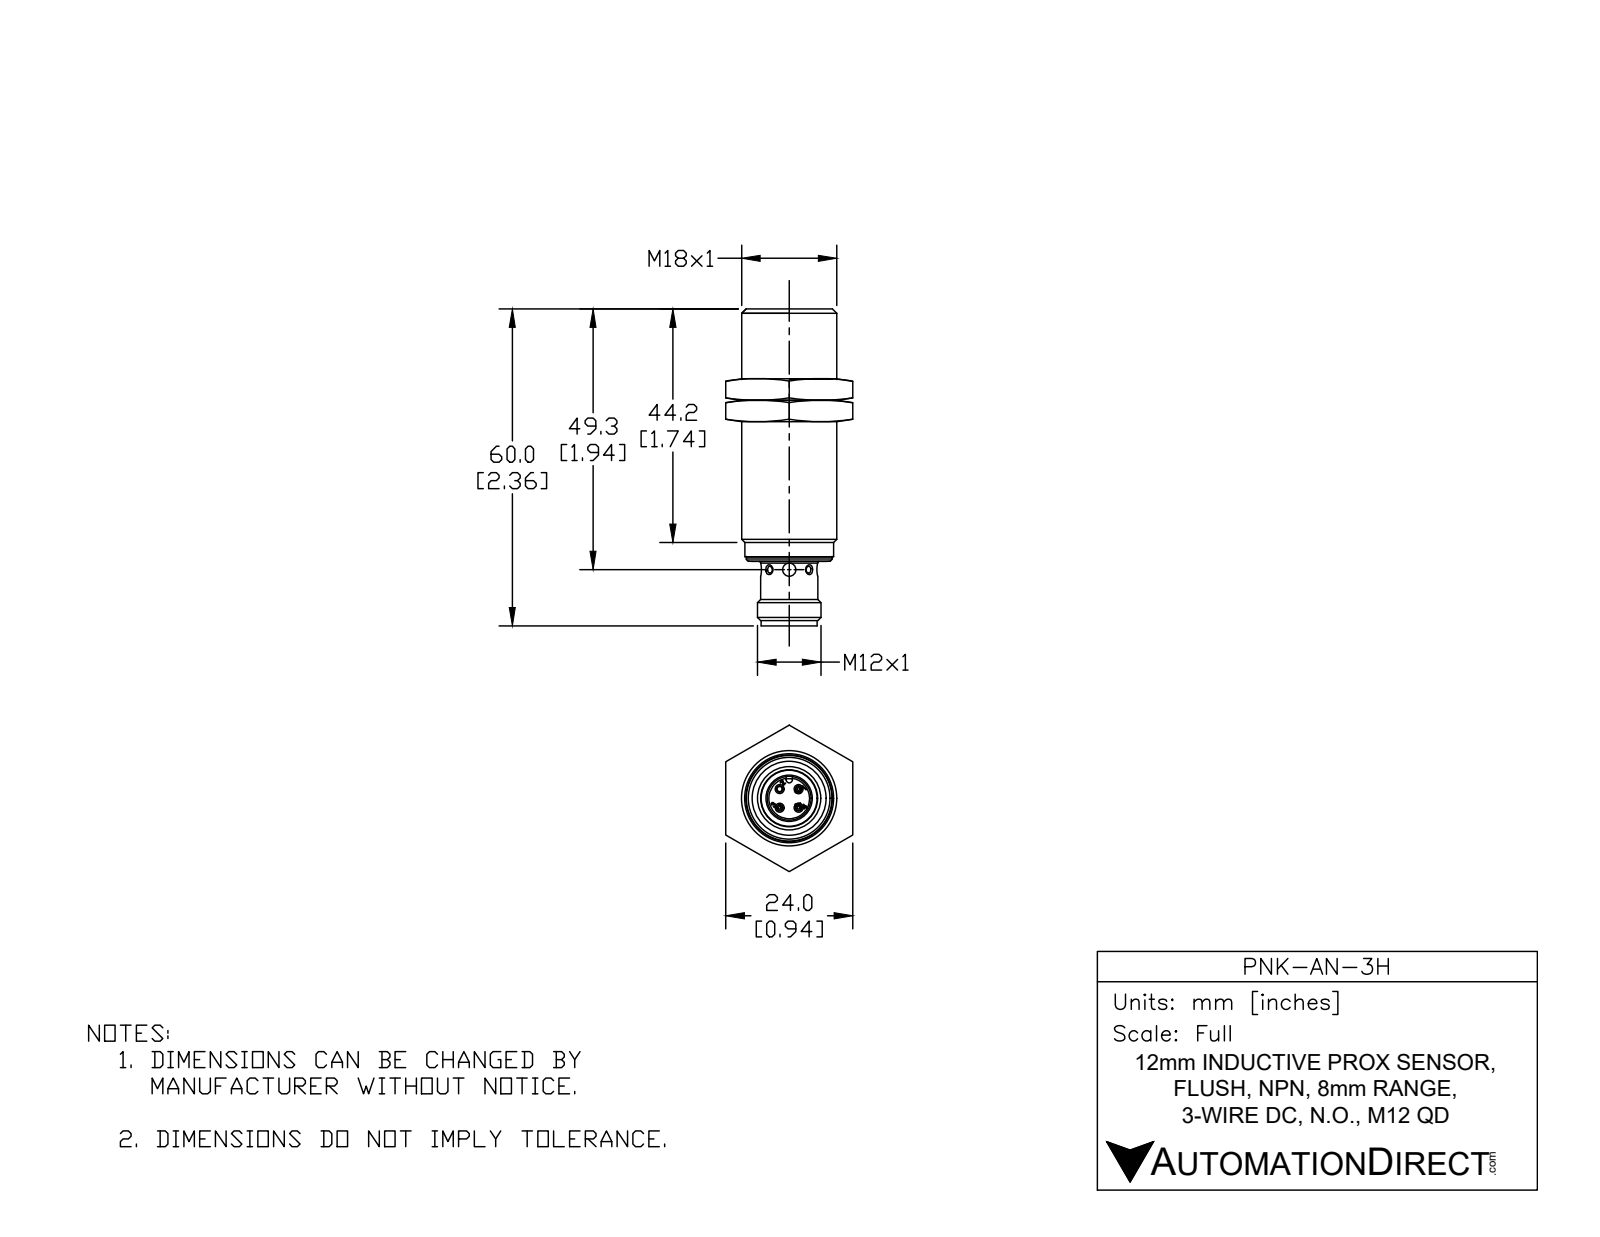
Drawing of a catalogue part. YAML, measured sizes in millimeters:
part_name: "PNK-AN-3H"
step_written_by: "SolidWorks 2017 (AUTOMOTIVE_DESIGN)"
units: millimeters
bodies: {solids: 1, faces: 1142, planar: 751, cylindrical: 150, other: 241}
overall_size: [60, 18, 18]
volume: 12200
surface_area: 9458
round_holes:
  - {diameter: 1.1, count: 3}
  - {diameter: 1, count: 2}
  - {diameter: 2.5, count: 2}
  - {diameter: 1, count: 1}
  - {diameter: 1, count: 1}
  - {diameter: 8.3, count: 1}
  - {diameter: 10, count: 1}
  - {diameter: 15.7, count: 1}
  - {diameter: 16.1, count: 1}
round_bosses_or_shafts:
  - {diameter: 1, count: 9}
  - {diameter: 18, count: 1}
  - {diameter: 16.6, count: 1}
  - {diameter: 16.2, count: 1}
  - {diameter: 16.1, count: 1}
  - {diameter: 15.6, count: 1}
  - {diameter: 15.4, count: 1}
  - {diameter: 15.2, count: 1}
partial_cylinders:
  - {radius: 0.1, count: 38}
  - {radius: 0.6, count: 1}
  - {radius: 0.8, count: 1}
  - {radius: 4.1, count: 1}
face_to_face_distances: [1, 0.6, 0.5, 47.5, 47.8, 47.2, 46.8, 46.9, 46.5, 59]
hole_center_spacings: [2.5, 3.5, 5]
